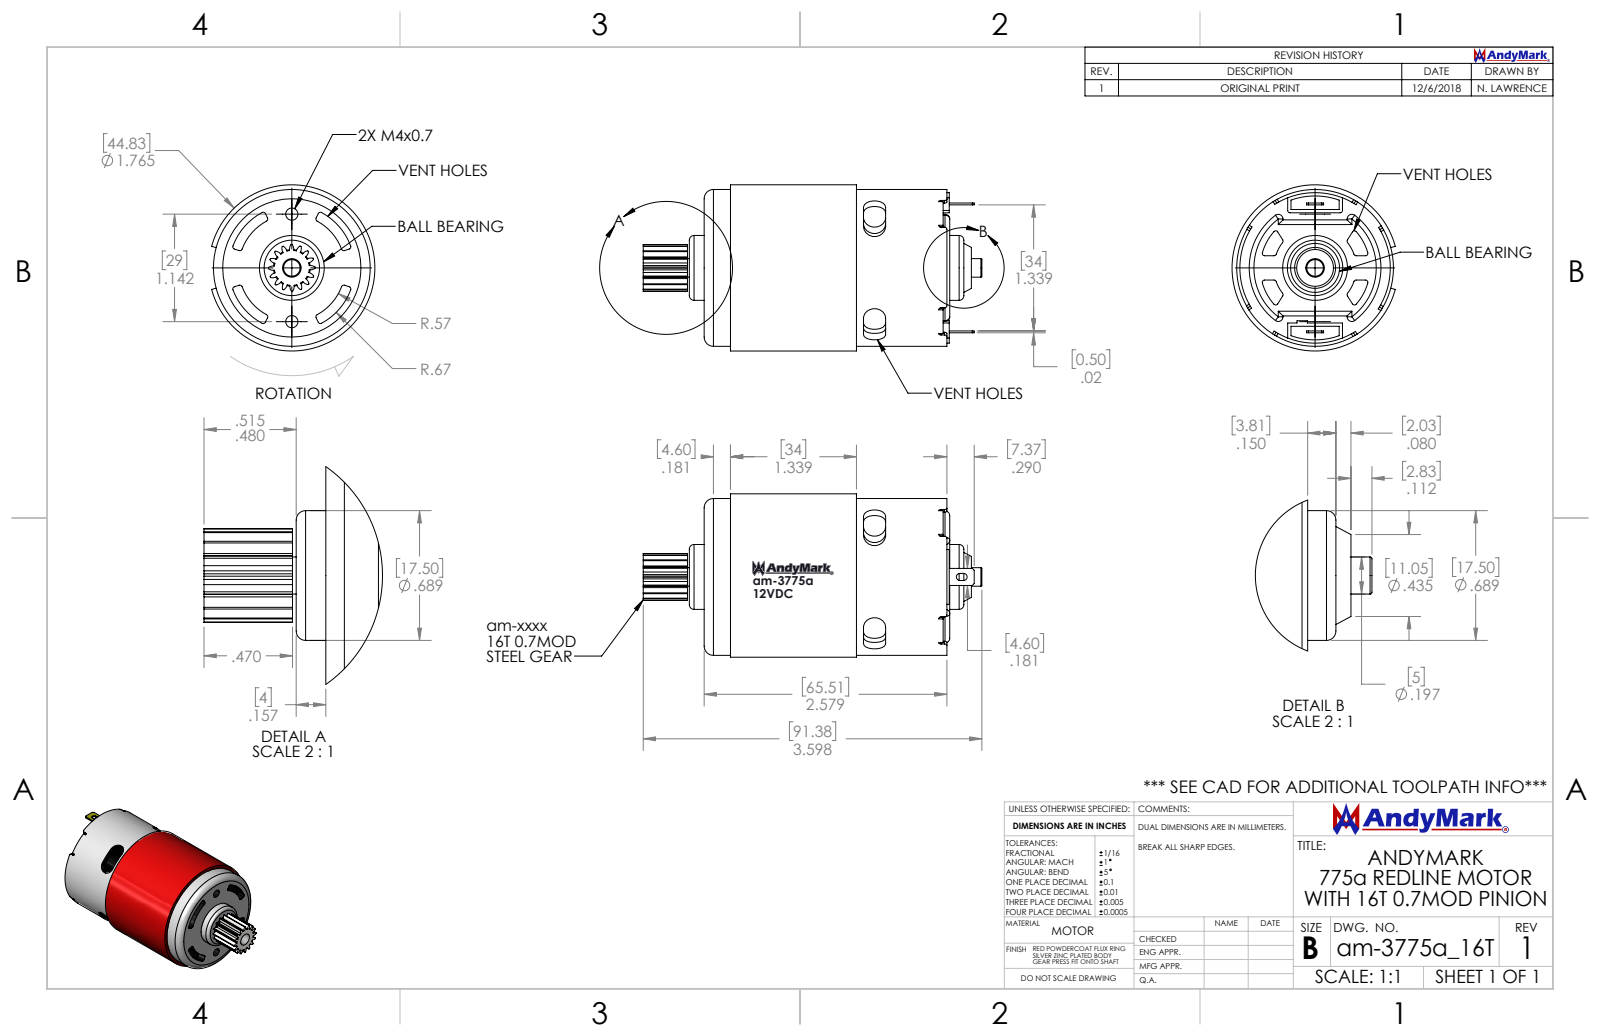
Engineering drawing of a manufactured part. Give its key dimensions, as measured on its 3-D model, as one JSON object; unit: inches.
{"part_name": "am-3775a_16T 775a RedLine with 16T Pinion", "step_written_by": "SolidWorks 2018 (AUTOMOTIVE_DESIGN)", "units": "inches", "bodies": {"solids": 2, "faces": 459, "planar": 144, "cylindrical": 202, "other": 113}, "overall_size": [3.598, 1.765, 1.735], "volume_in3": 3.235, "surface_area_in2": 37.96, "round_holes": [[0.13, 2], [0.39, 1], [1.494, 1]], "round_bosses_or_shafts": [[1.765, 1], [1.665, 1], [0.689, 1], [0.197, 1]], "partial_cylinders_radius": [[0.025, 50], [0.088, 32], [0.05, 8], [0.059, 8], [0.037, 2], [0.117, 2], [0.117, 2], [0.186, 1]], "face_to_face_distances": [0.1, 0.11, 1.64, 1.74, 1.75, 2.428, 0.788, 0.688, 0.678, 0.181], "hole_center_spacings": [0.571, 1.142]}
